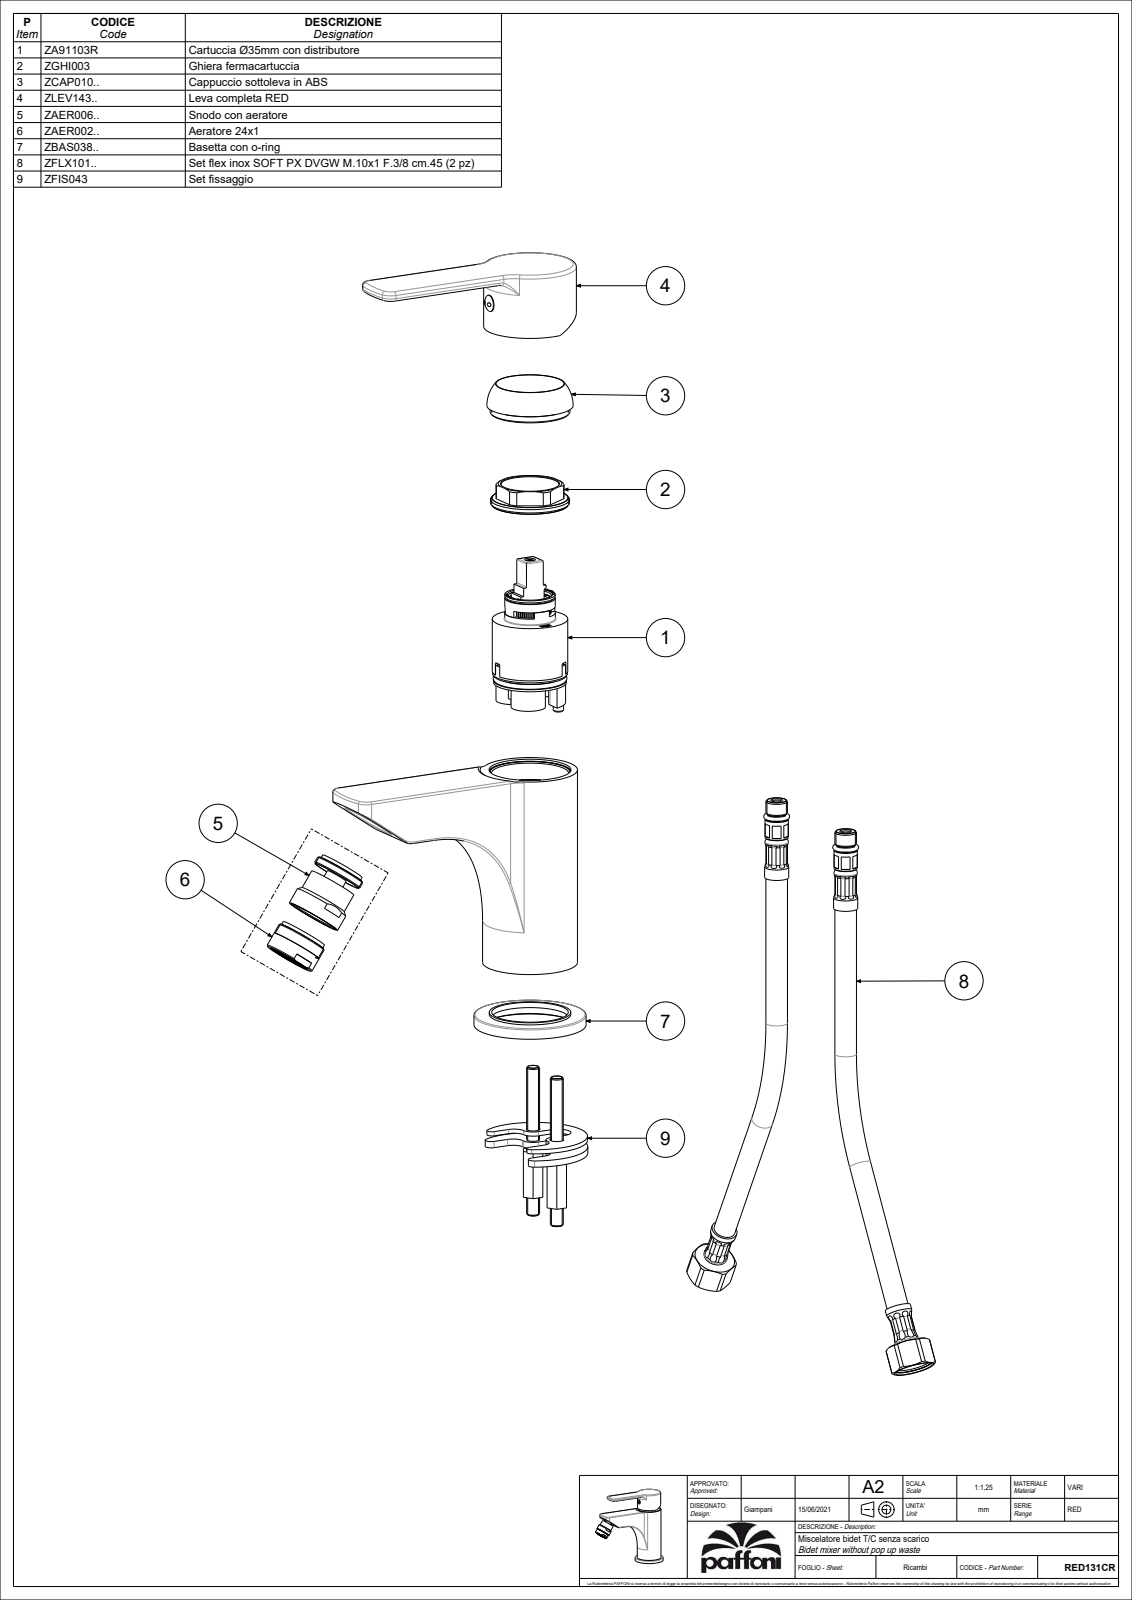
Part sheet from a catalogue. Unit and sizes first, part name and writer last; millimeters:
Units: millimetres
Overall size (bounding box): 138.72 × 130.73 × 52
Round holes (diameter × count): ⌀9 ×5, ⌀5 ×3, ⌀8 ×3, ⌀12 ×3, ⌀3.3 ×2, ⌀4 ×2, ⌀5.5 ×2, ⌀6 ×2, ⌀11 ×2, ⌀16 ×2, ⌀3 ×1, ⌀3.5 ×1
Round bosses / shafts (diameter × count): ⌀4.8 ×2, ⌀52 ×1, ⌀44 ×1, ⌀43 ×1, ⌀42.6 ×1, ⌀37.8 ×1, ⌀35 ×1, ⌀34.8 ×1
Partial cylindrical surfaces — rounded edges, fillets, slot ends (radius × count): R0.5 ×100, R0.15 ×11, R1 ×10, R0.3 ×9, R5 ×6, R10 ×5, R1.5 ×4, R2 ×4
Main face-to-face distances: 3.5, 27.5, 28, 31, 4.5, 31.5, 1, 3, 36, 32.5
Hole centre spacings: 13.6, 0.71, 2.83, 8.51, 8.6, 9.66, 9.85, 11.18
Volume: 139 813 mm³ · Surface area: 91 124 mm²
Bodies: 2 solids, 2915 faces (2111 planar, 458 cylindrical, 346 other)
Part name (STEP PRODUCT): RED131CR
STEP written by: CREO PARAMETRIC BY PTC INC, 2020044 (CONFIG_CONTROL_DESIGN)
